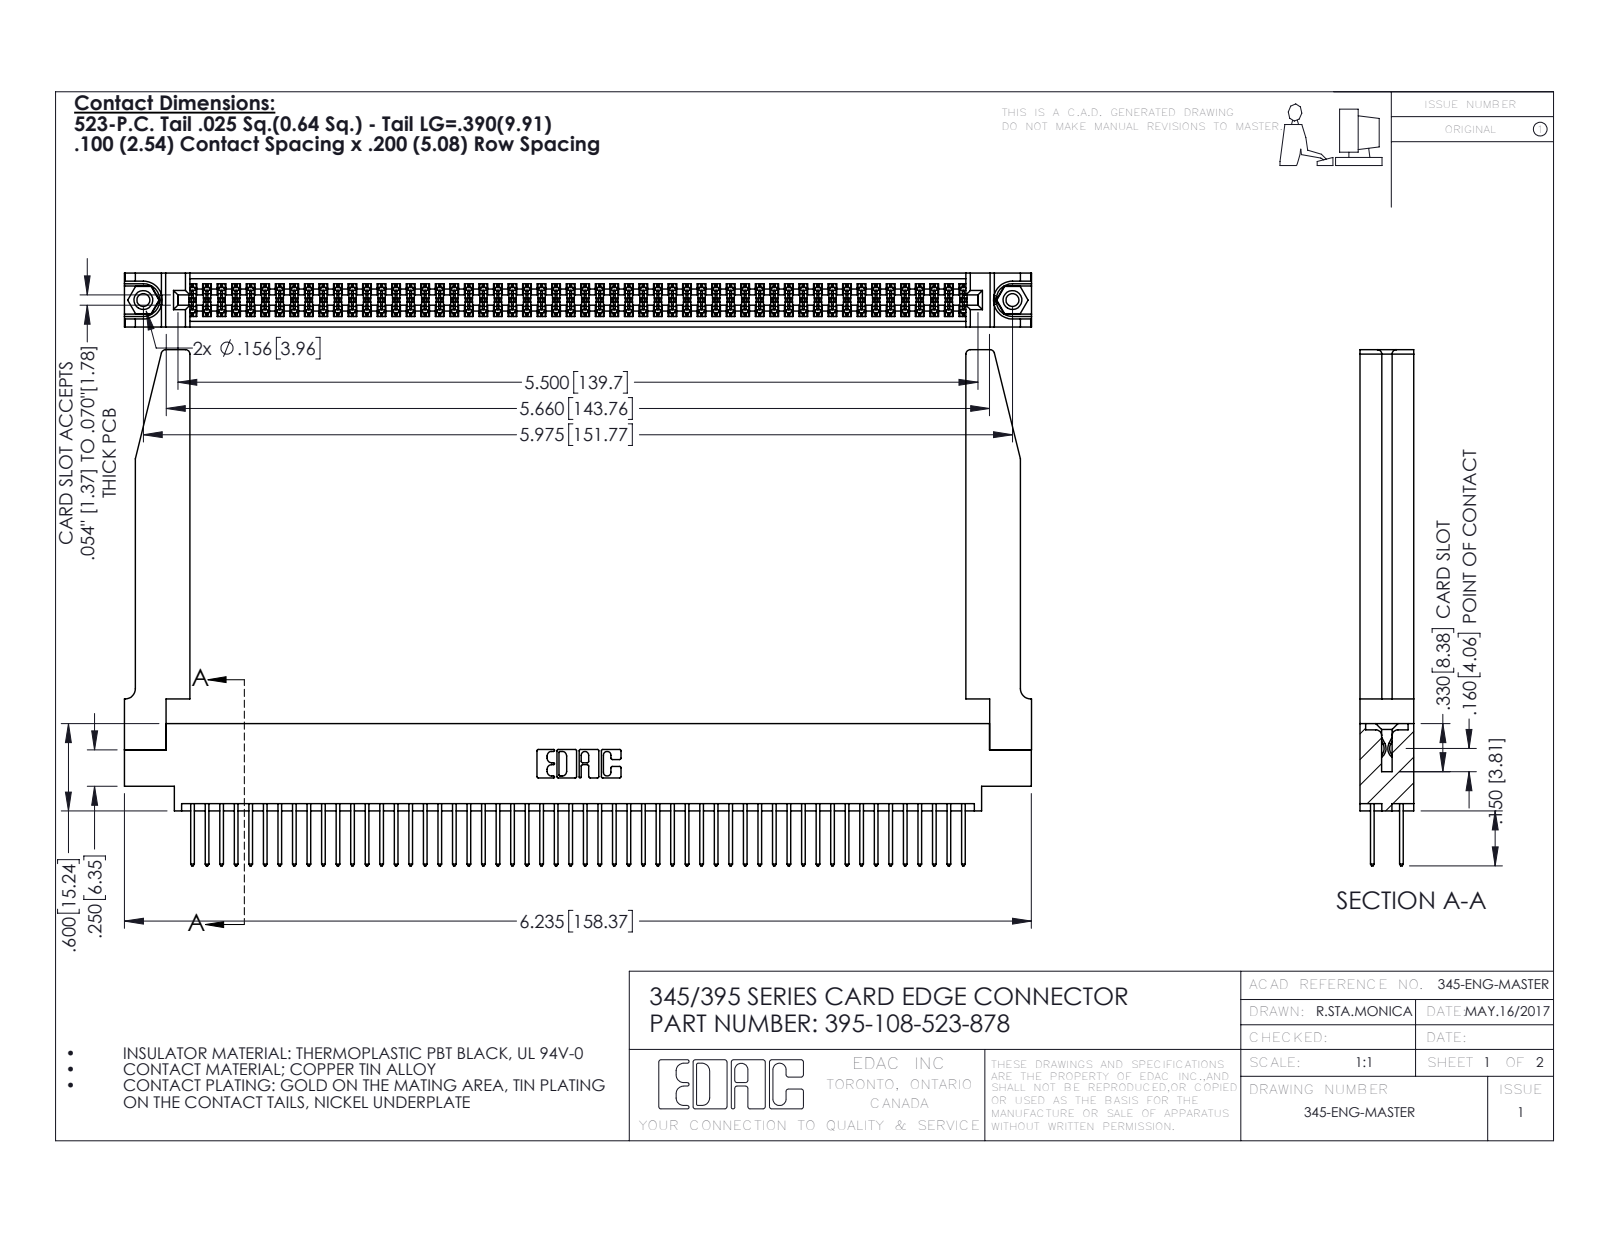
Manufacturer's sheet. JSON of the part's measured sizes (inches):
{"part_name": "345 Part_0.170 Offset - 0.156 Dia-TH; 345-250-001_345-250-001-102; 345-292-001_345-293-123; 395-108-523-878 (+1 more)", "step_written_by": "SolidWorks 2016 (CONFIG_CONTROL_DESIGN)", "units": "inches", "bodies": {"solids": 113, "faces": 5764, "planar": 3790, "cylindrical": 1922, "other": 52}, "overall_size": [6.236, 3.547, 0.37], "volume_in3": 1.427, "surface_area_in2": 48.48, "round_holes": [[0.089, 2], [0.125, 2], [0.156, 2], [0.064, 1]], "round_bosses_or_shafts": [[0.155, 2]], "partial_cylinders_radius": [[0.006, 162], [0.01, 108], [0.01, 22], [0.03, 8], [0.007, 6], [0.031, 6], [0.026, 3], [0.014, 2]], "face_to_face_distances": [0.072, 0.298, 0.37, 0.098, 0.272, 0.025, 0.2, 0.225, 0.175, 0.148], "hole_center_spacings": [0.27, 5.739, 5.975]}
